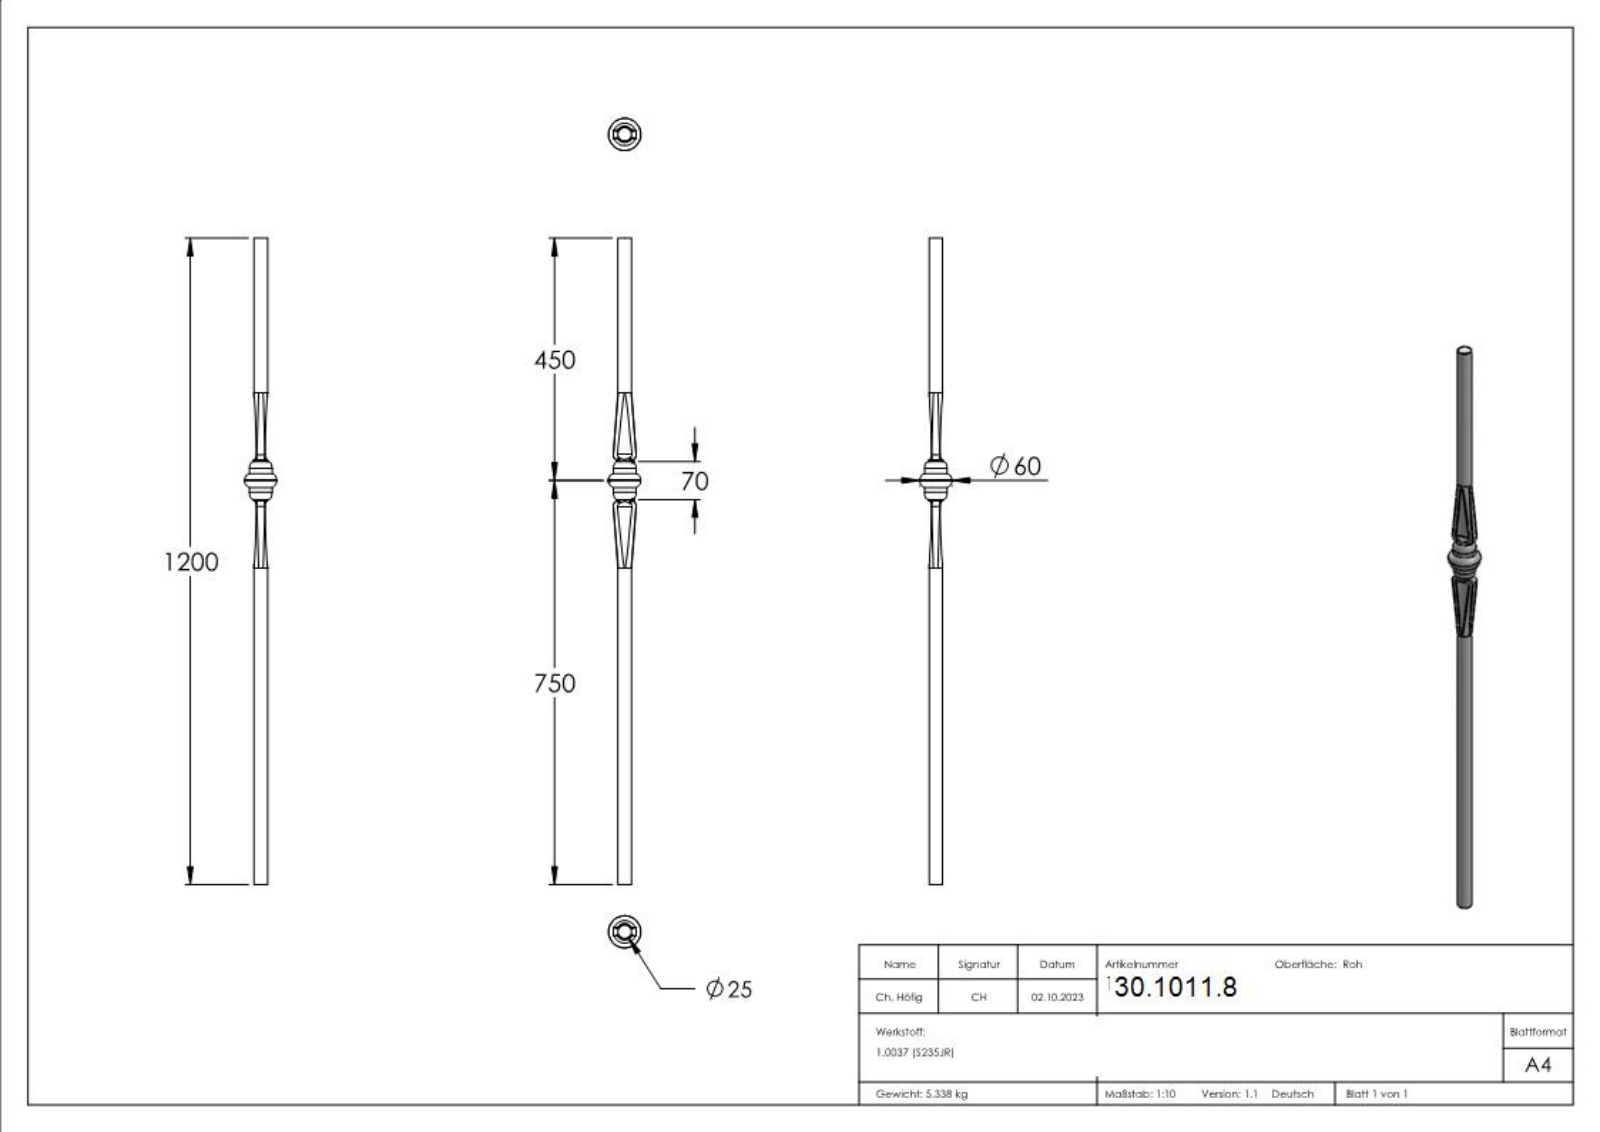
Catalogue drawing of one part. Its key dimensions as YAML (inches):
part_name: "1016"
step_written_by: "SolidWorks 2018 (CONFIG_CONTROL_DESIGN)"
units: inches
bodies: {solids: 2, faces: 75, planar: 4, cylindrical: 7, other: 64}
overall_size: [47.244, 2.362, 2.362]
volume: 41.77
surface_area: 184.7
round_holes:
  - {diameter: 1.122, count: 1}
round_bosses_or_shafts:
  - {diameter: 2.362, count: 1}
  - {diameter: 1.654, count: 1}
  - {diameter: 1.102, count: 1}
  - {diameter: 0.984, count: 1}
face_to_face_distances: [47.244, 30.906, 16.339, 28.15, 2.756, 19.094]
